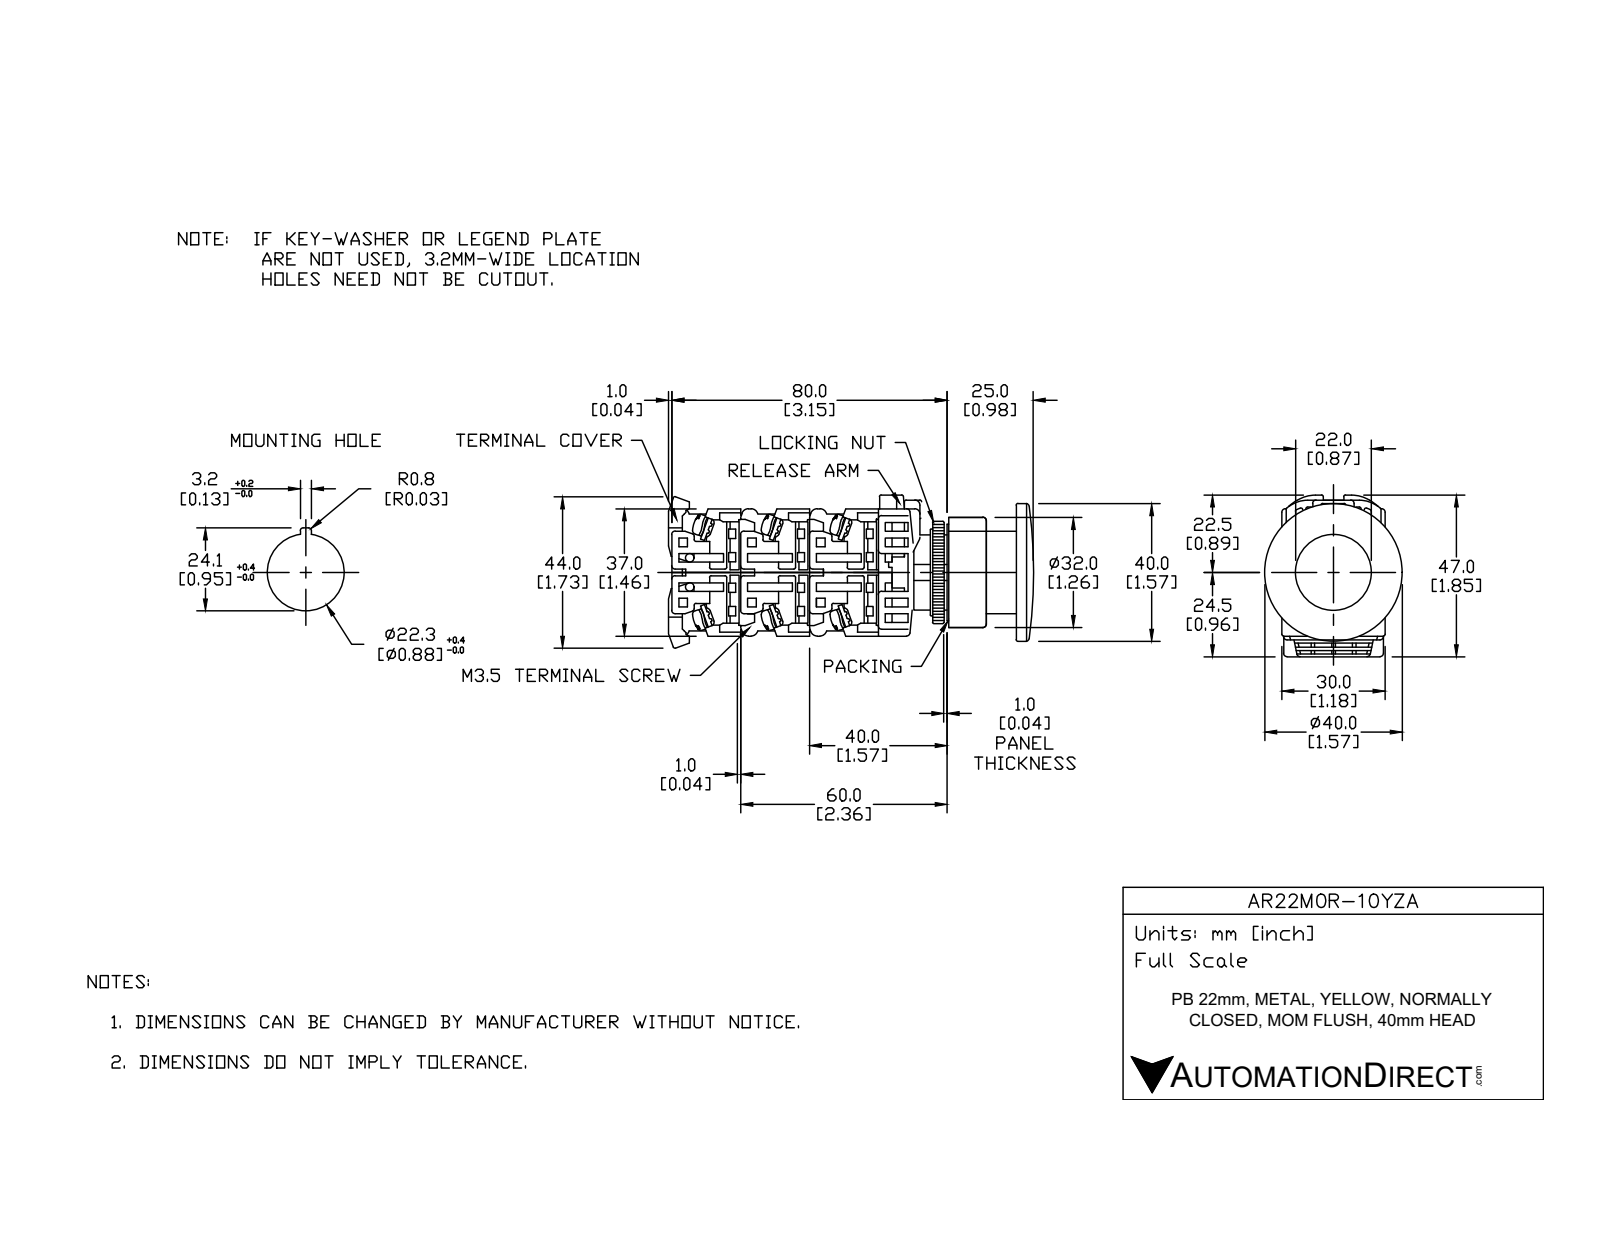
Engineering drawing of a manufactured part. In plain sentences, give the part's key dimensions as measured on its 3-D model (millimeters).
The part is named "AR22M0R-10YZA". Its 3-D file was written by "SolidWorks 2017 (AUTOMOTIVE_DESIGN)". It is 12 solids with 304 faces: 202 planar, 76 cylindrical and 26 other. Overall it measures 66.5 by 43 by 40 millimeters. Its volume is 37 326 cubic millimeters and its surface area 22 079 square millimeters. Round holes: 1 of diameter 21.8, 1 of diameter 22, 1 of diameter 25, 1 of diameter 31. Round bosses or shafts: 2 of diameter 5, 1 of diameter 40, 1 of diameter 32, 1 of diameter 30.5, 1 of diameter 29.8, 1 of diameter 24, 1 of diameter 23.8, 1 of diameter 21.75. Partial cylindrical surfaces (rounded edges, fillets, slot ends): 23 of radius 0.5, 4 of radius 1.75, 4 of radius 5, 2 of radius 4, 1 of radius 16.59, 1 of radius 17.59. The main face-to-face distances are 1, 10, 28.5, 18, 38.5, 21, 3, 2, 29, 7.5.
